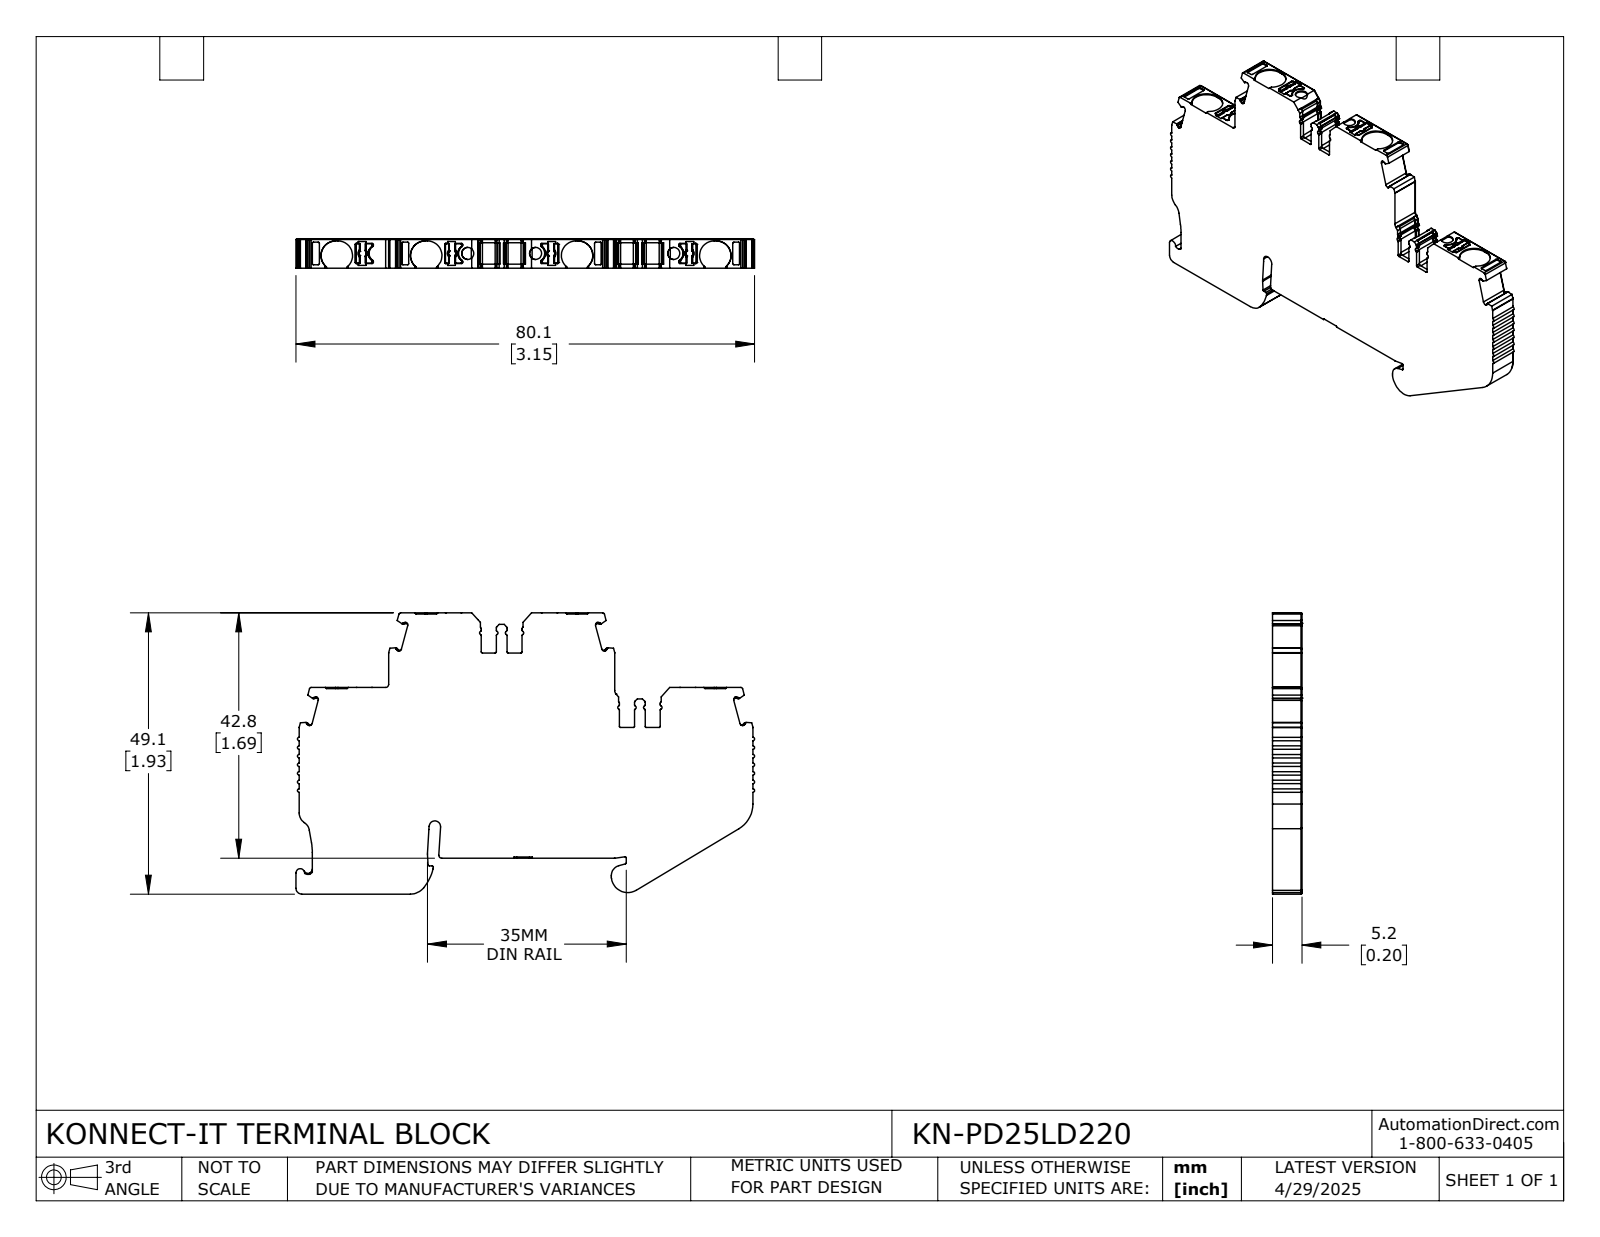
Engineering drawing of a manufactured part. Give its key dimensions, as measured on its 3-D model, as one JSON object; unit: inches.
{"part_name": "KN-PD25LD220", "step_written_by": "SolidWorks 2024 (CONFIG_CONTROL_DESIGN)", "units": "inches", "bodies": {"solids": 1, "faces": 979, "planar": 470, "cylindrical": 438, "other": 71}, "overall_size": [3.153, 1.933, 0.203], "volume_in3": 0.889, "surface_area_in2": 11.63, "round_holes": [[0.083, 3]], "partial_cylinders_radius": [[0.008, 100], [0.012, 57], [0.004, 41], [0.02, 21], [0.016, 17], [0.006, 16], [0.024, 9], [0.006, 8]], "face_to_face_distances": [0.203, 0.512, 0.246, 1.678, 1.166, 1.924, 0.079, 1.412, 0.504, 0.95], "hole_center_spacings": [0.466, 0.95, 1.417]}
